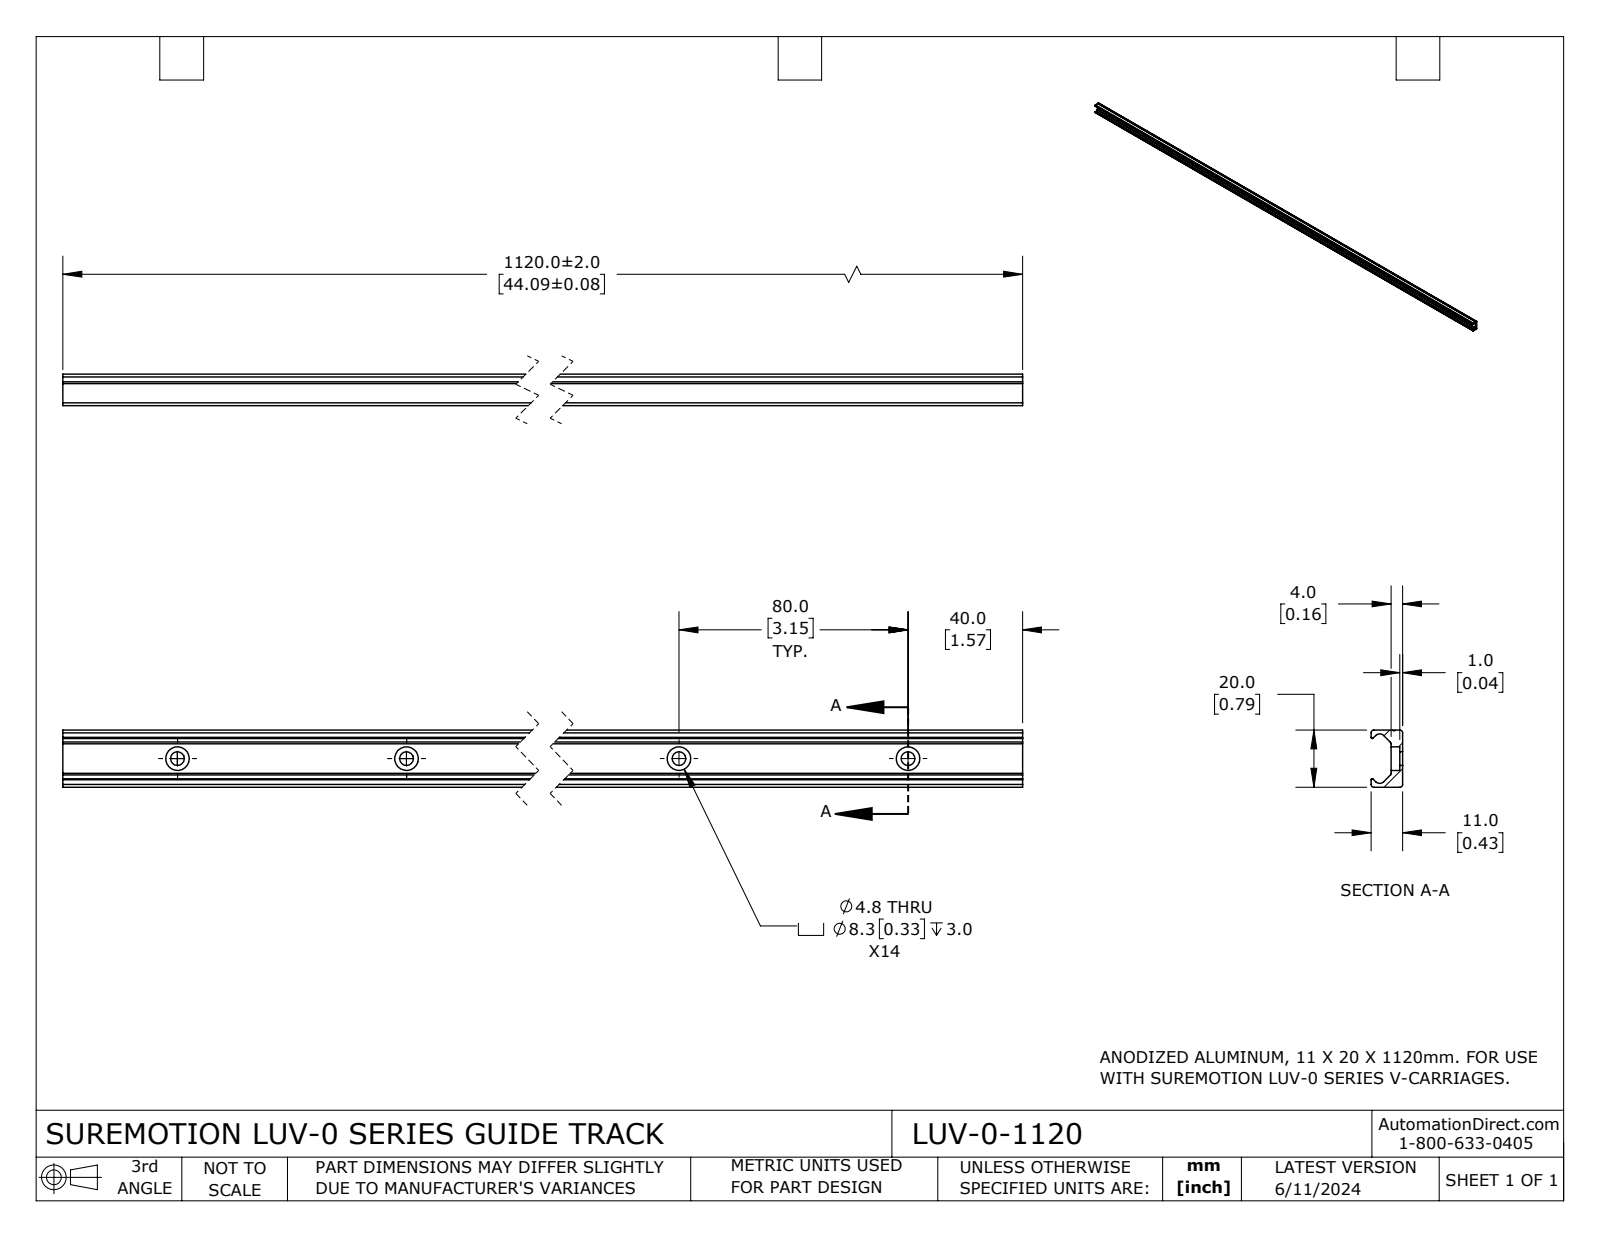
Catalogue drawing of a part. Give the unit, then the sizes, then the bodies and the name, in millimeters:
Units: millimetres
Overall size (bounding box): 1120 × 19.99 × 11
Round holes (diameter × count): ⌀4.8 ×14, ⌀8.25 ×7, ⌀8.26 ×7
Partial cylindrical surfaces — rounded edges, fillets, slot ends (radius × count): R0.99 ×4, R0.38 ×2, R0.4 ×2, R0.79 ×2, R1.98 ×2, R0.33 ×1
Main face-to-face distances: 4.01, 20, 11, 6.99, 13.4, 1.01, 3, 9.99, 1120
Hole centre spacings: 80, 160, 240, 320, 400, 480, 560, 640
Volume: 123 614 mm³ · Surface area: 84 778 mm²
Bodies: 1 solid, 96 faces (27 planar, 69 cylindrical, 0 other)
Part name (STEP PRODUCT): LUV-0-1120
STEP written by: SolidWorks 2023 (CONFIG_CONTROL_DESIGN)
